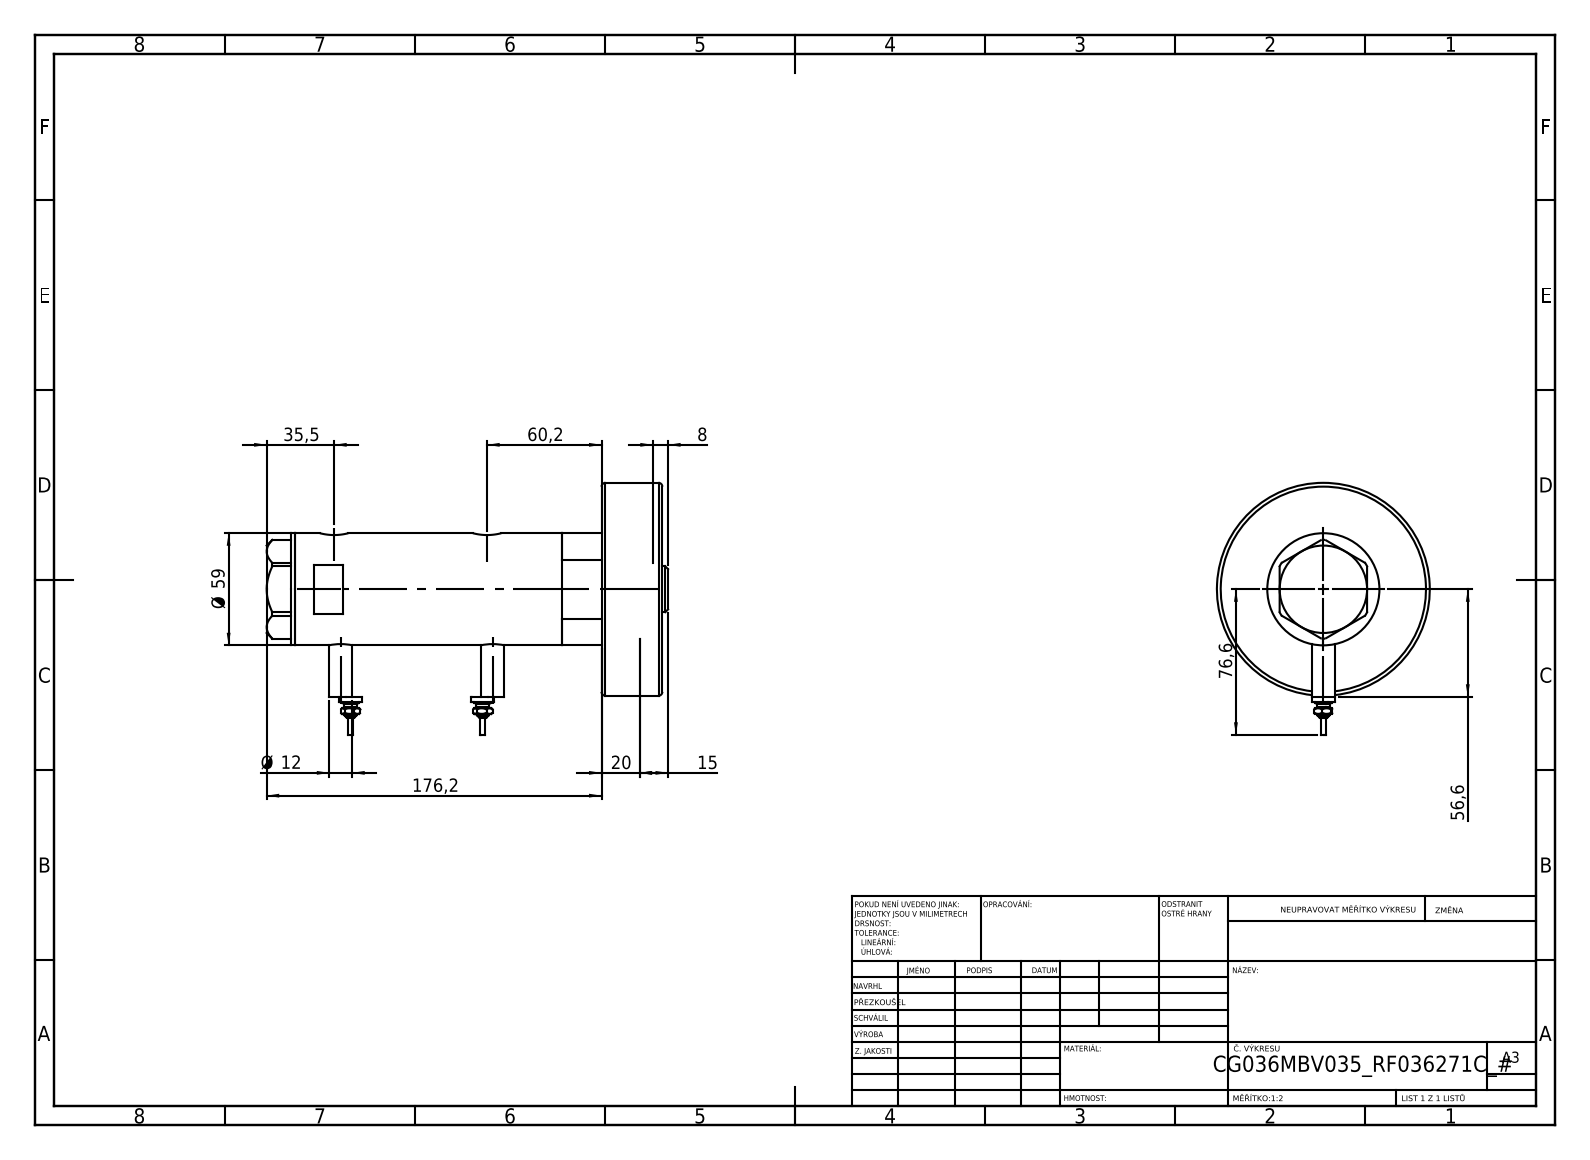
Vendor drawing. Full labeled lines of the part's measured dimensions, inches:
Part name (STEP PRODUCT): V270CG_271C; V270CG_FRONT; V270CG_BACK; Switch (+2 more)
STEP written by: SolidWorks 2019 (CONFIG_CONTROL_DESIGN)
Units: inches
Bodies: 7 solids, 222 faces (81 planar, 73 cylindrical, 68 other)
Overall size (bounding box): 8.315 × 5.22 × 4.409
Volume: 45.71 in³ · Surface area: 209 in²
Round holes (diameter × count): ⌀0.383 ×2, ⌀0.492 ×2, ⌀0.591 ×2, ⌀0.335 ×1, ⌀0.984 ×1, ⌀1.043 ×1, ⌀1.417 ×1, ⌀1.575 ×1, ⌀1.89 ×1, ⌀2.047 ×1
Round bosses / shafts (diameter × count): ⌀0.472 ×4, ⌀0.354 ×2, ⌀0.276 ×2, ⌀0.177 ×2, ⌀0.098 ×2, ⌀4.409 ×1, ⌀2.323 ×1, ⌀1.811 ×1
Main face-to-face distances: 1.26, 6.346, 7.606, 4.024, 2.323, 3.583, 0.925, 3.098, 5.421, 6.681
Hole centre spacings: 0.114, 0.138, 3.031, 3.146, 3.169, 3.283
